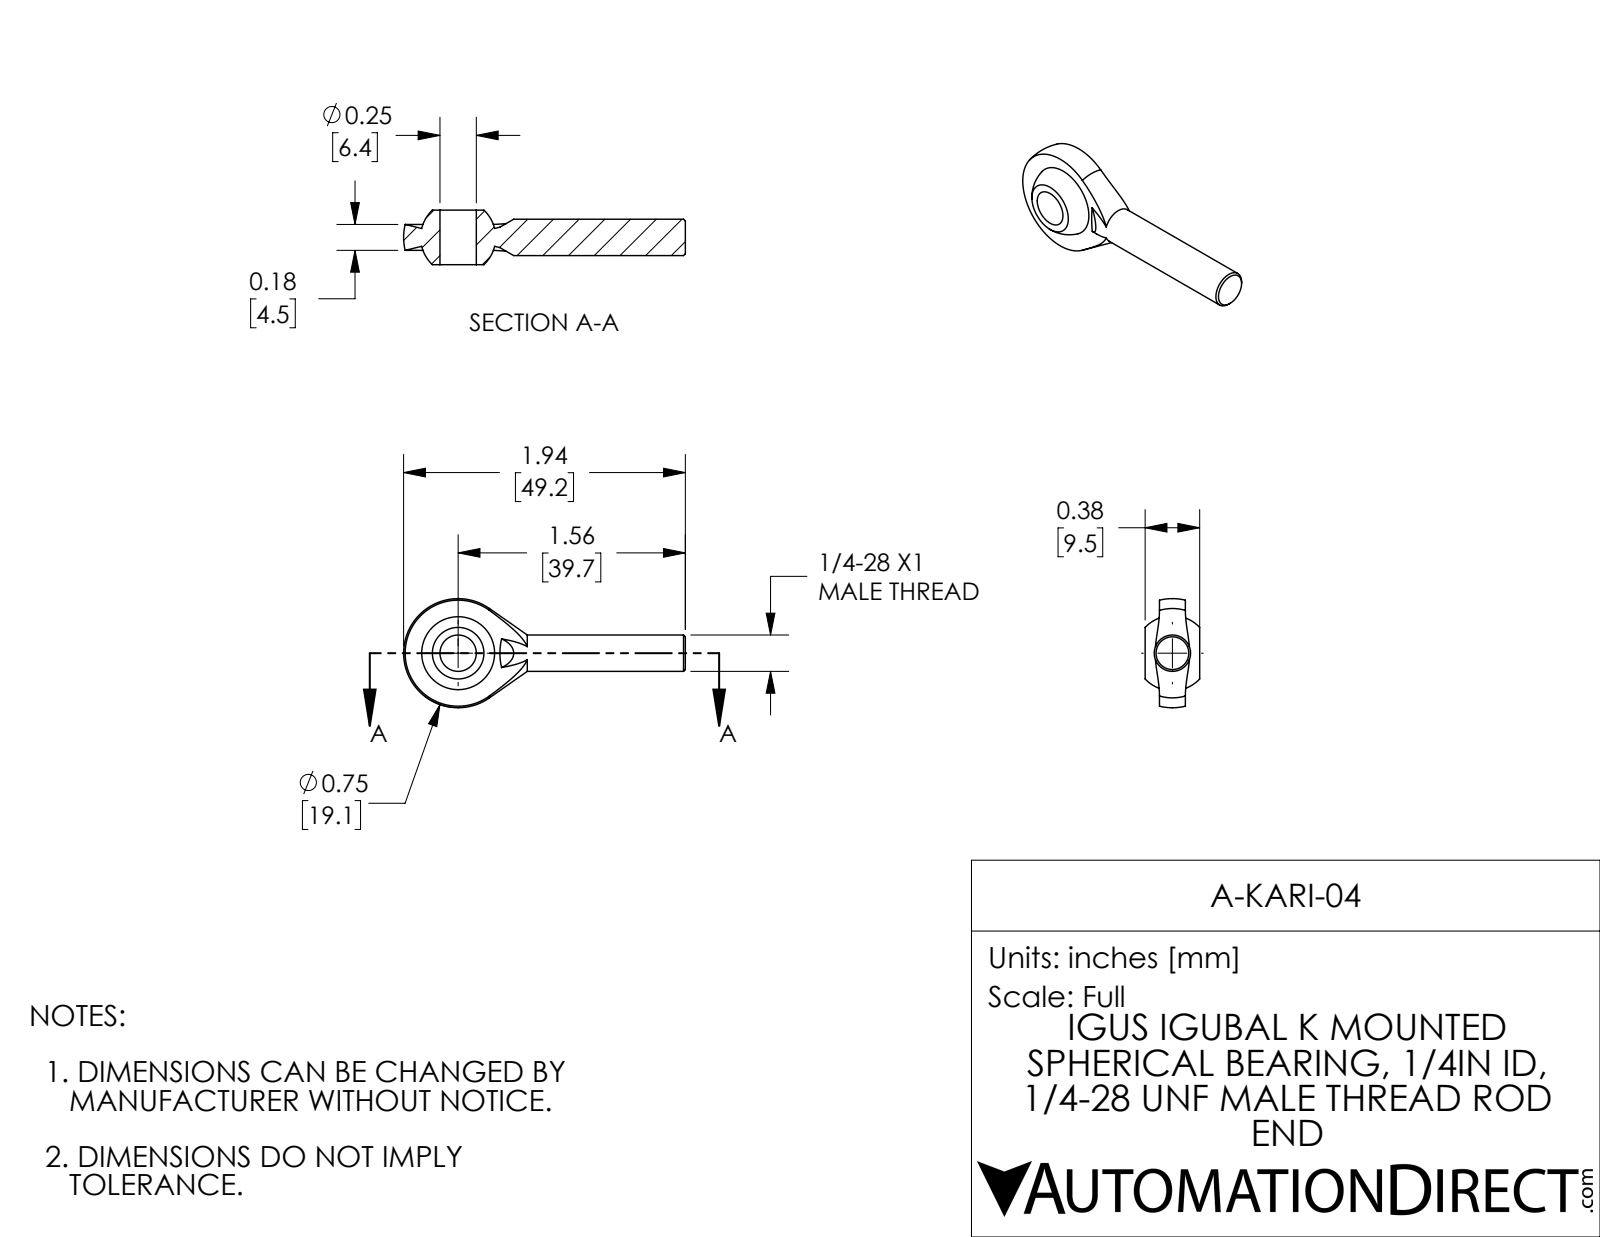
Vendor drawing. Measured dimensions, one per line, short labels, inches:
name: A-KARI-04
written by: SolidWorks 2017 (AUTOMOTIVE_DESIGN)
unit: in
bodies: 1 solid, 25 faces (5 planar, 4 cylindrical, 16 other)
size: 1.926 × 0.75 × 0.375
volume: 0.144 in³; area: 2.657 in²
holes: 1× ⌀0.25
bosses: 1× ⌀0.25
face distances: 0.375
